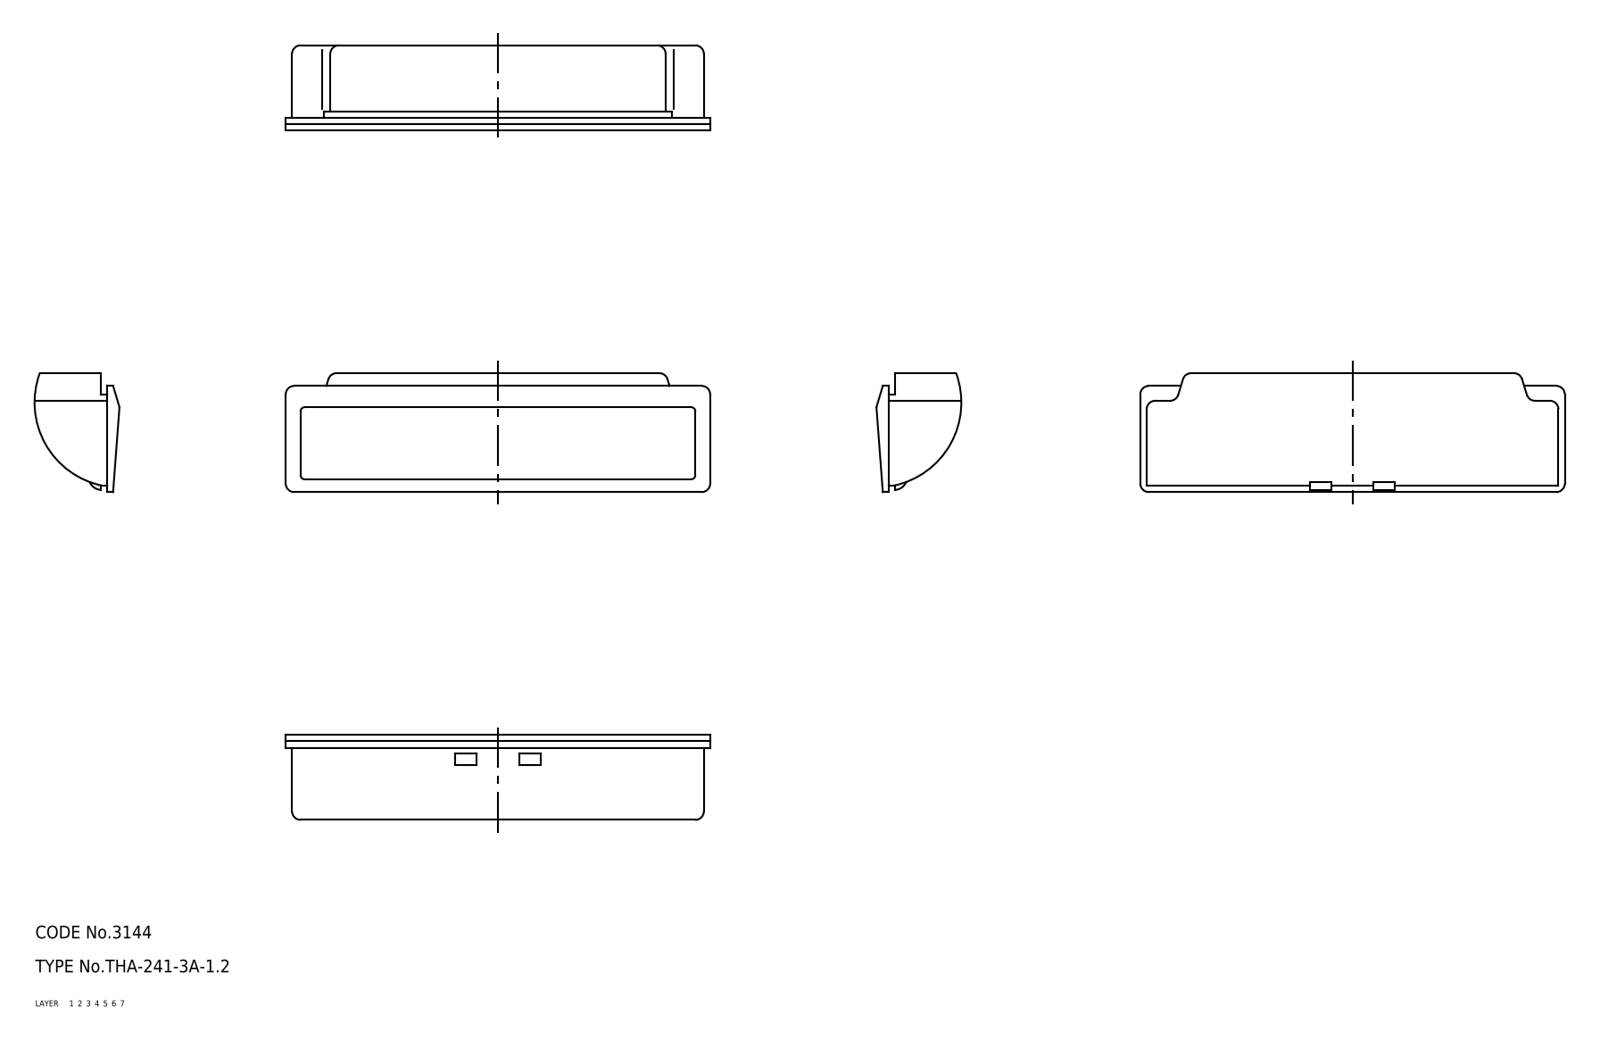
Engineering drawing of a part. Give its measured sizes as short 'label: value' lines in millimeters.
name: pull
written by: CADfix (AUTOMOTIVE_DESIGN)
unit: mm
bodies: 1 solid, 64 faces (0 planar, 0 cylindrical, 64 other)
size: 100 × 28 × 20
volume: 11 667 mm³; area: 13 236 mm²
